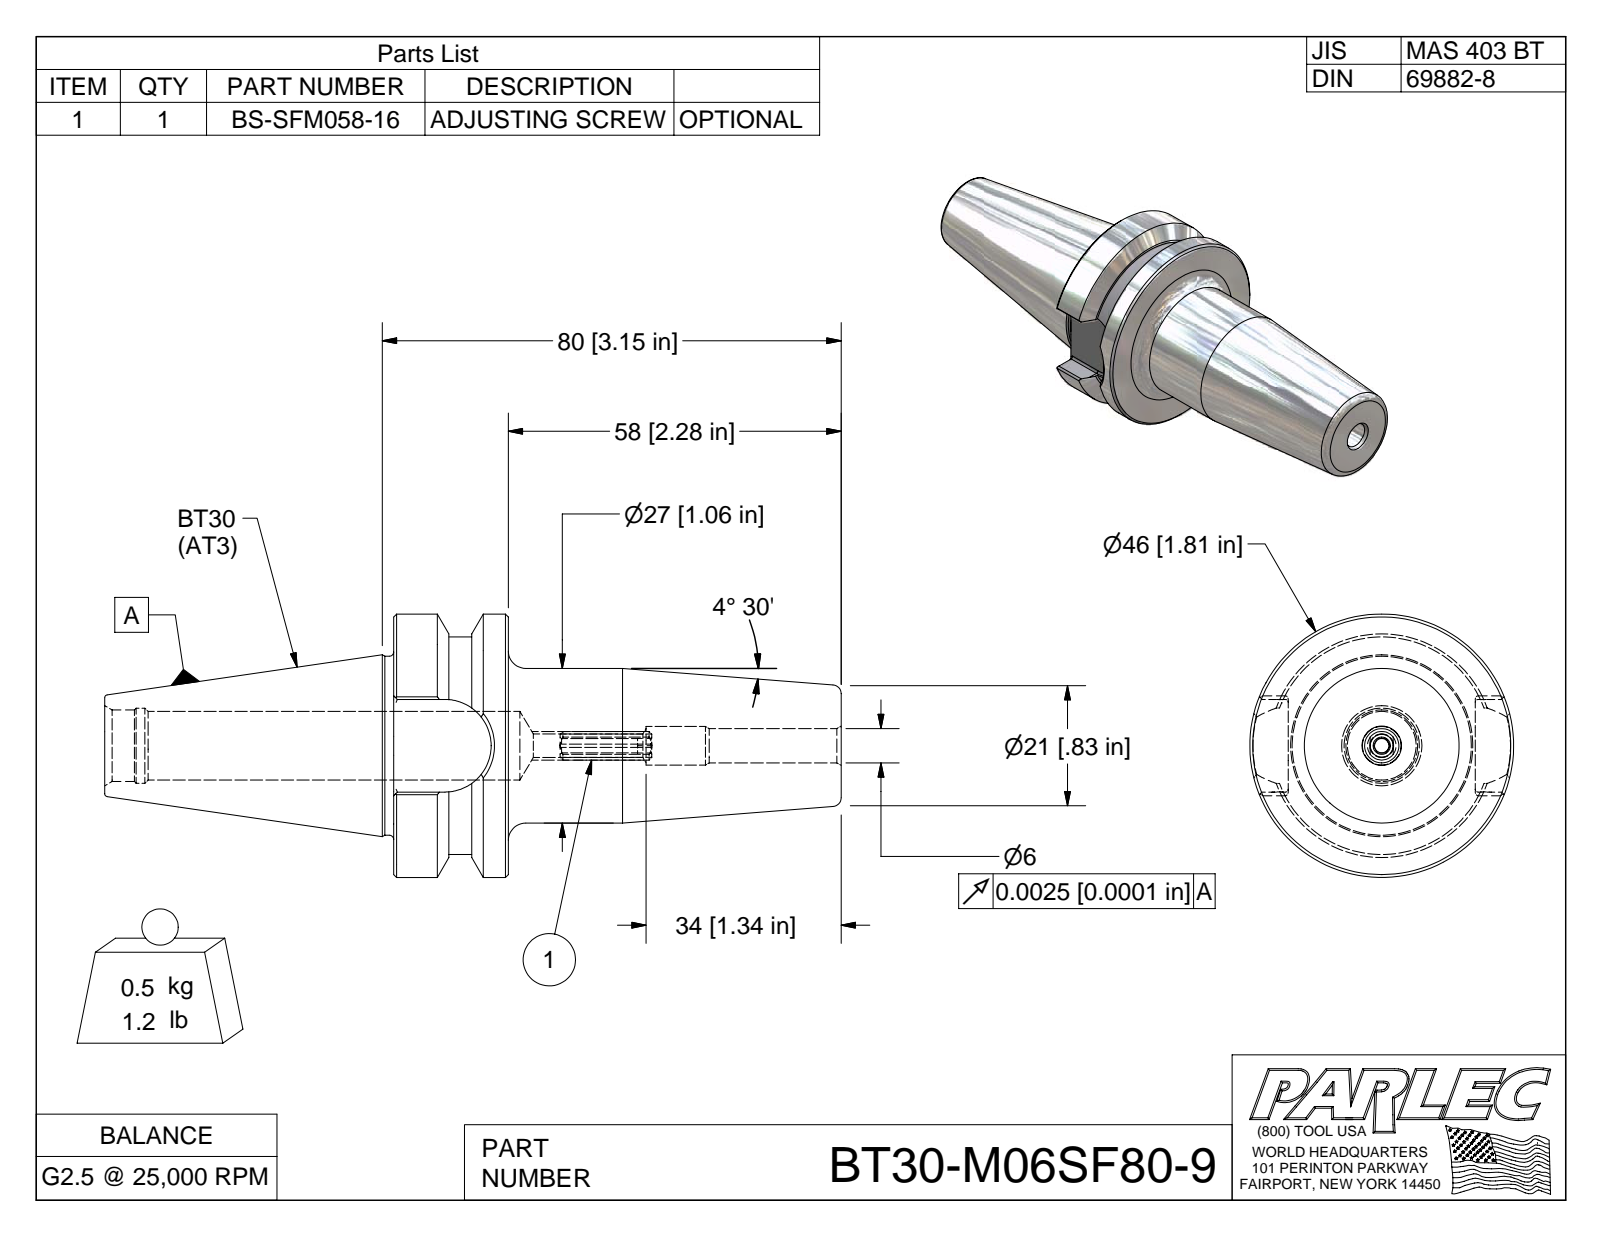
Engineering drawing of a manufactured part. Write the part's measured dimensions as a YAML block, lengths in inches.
part_name: "BT30-M06SF80-9; BT30-M06SF80-9-1; BS-SFM058-16"
step_written_by: "Autodesk Inventor 2009 (AUTOMOTIVE_DESIGN)"
units: inches
bodies: {solids: 2, faces: 92, planar: 35, cylindrical: 22, other: 35}
overall_size: [5.056, 1.811, 1.811]
volume: 4.419
surface_area: 28.35
round_holes:
  - {diameter: 0.236, count: 1}
  - {diameter: 0.266, count: 1}
  - {diameter: 0.517, count: 1}
round_bosses_or_shafts:
  - {diameter: 1.811, count: 1}
  - {diameter: 1.23, count: 1}
  - {diameter: 1.063, count: 1}
partial_cylinders:
  - {radius: 0.02, count: 8}
  - {radius: 0.098, count: 1}
  - {radius: 0.319, count: 1}
  - {radius: 0.748, count: 1}
face_to_face_distances: [0.787, 1.283, 3.072, 2.285, 0.563, 0.72, 0.157, 1.984, 2.771, 5.056]
